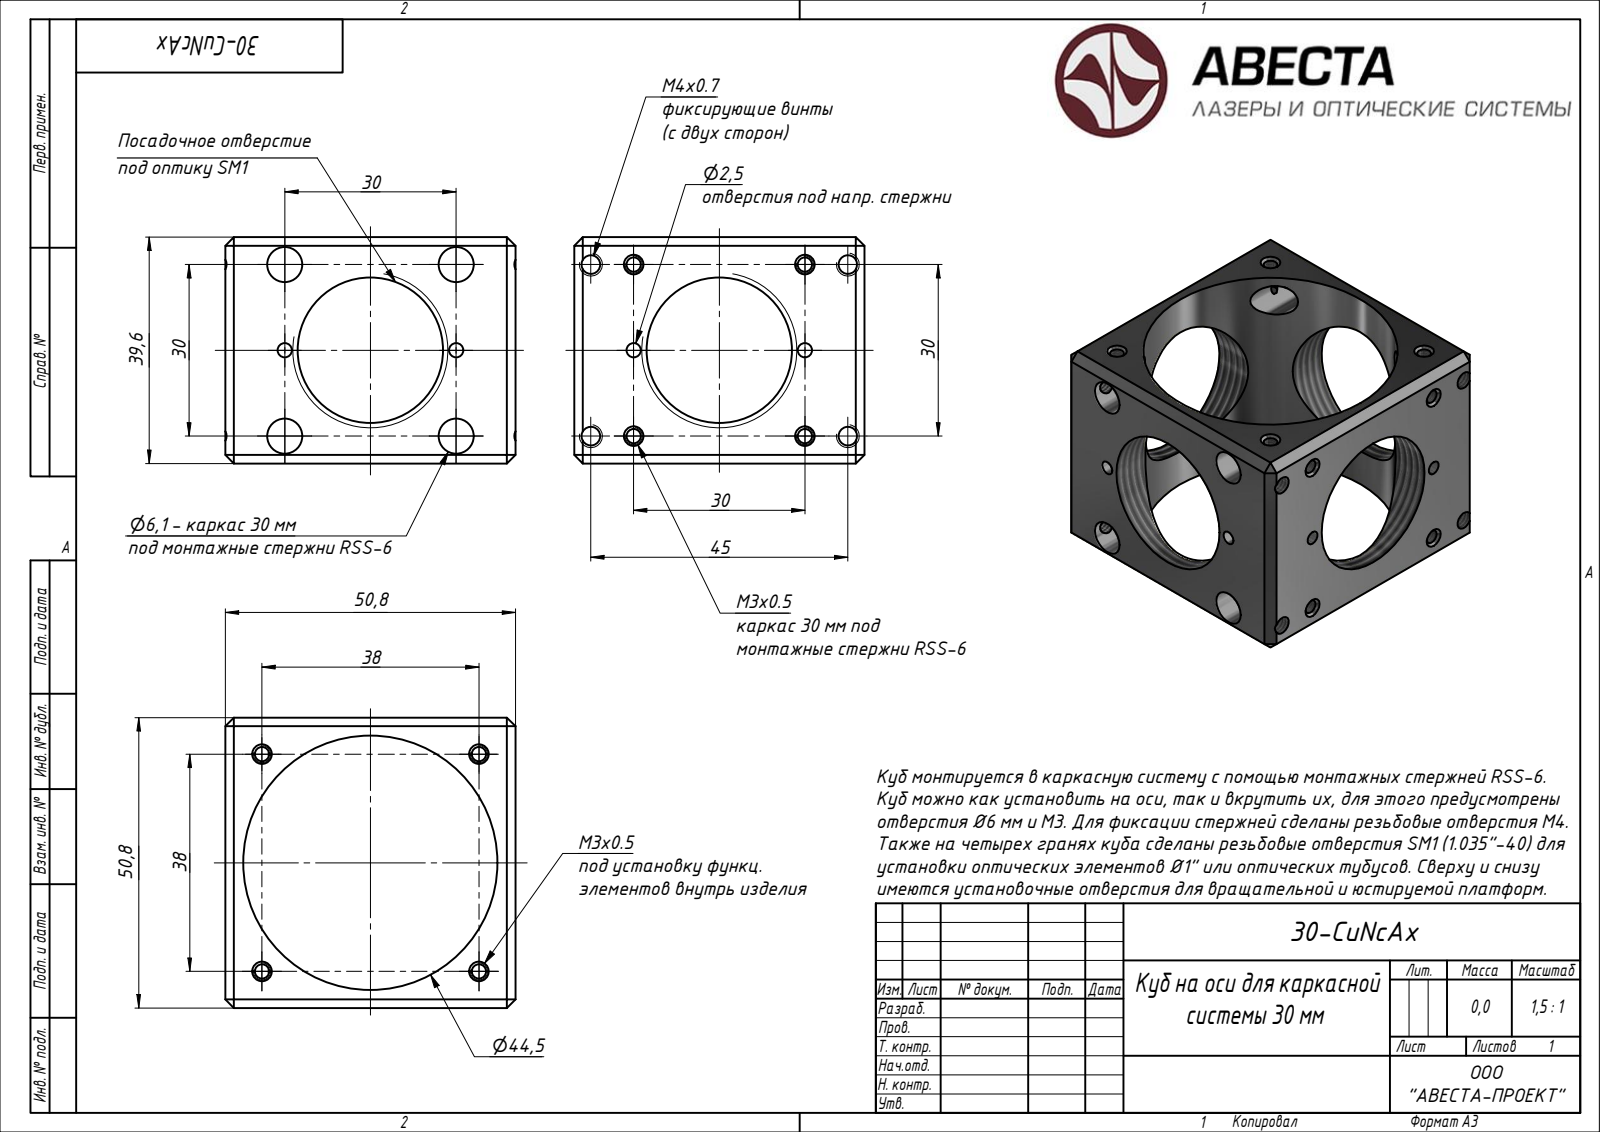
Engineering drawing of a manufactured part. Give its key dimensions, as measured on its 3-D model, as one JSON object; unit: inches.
{"part_name": "30-Cu2", "step_written_by": "Autodesk Inventor 2020 (AUTOMOTIVE_DESIGN)", "units": "inches", "bodies": {"solids": 1, "faces": 111, "planar": 50, "cylindrical": 45, "other": 16}, "overall_size": [2, 2, 1.559], "volume_in3": 1.727, "surface_area_in2": 23.19, "round_holes": [[0.097, 8], [0.098, 4], [0.128, 4], [0.24, 4], [1.003, 2], [1.752, 1]], "face_to_face_distances": [2, 1.559, 2.433, 2.745, 0.236, 1.764, 1.528, 1.323, 1.087, 3.071], "hole_center_spacings": [0.591, 1.181, 0.835, 1.32, 0.295, 0.66, 1.058, 1.065]}
